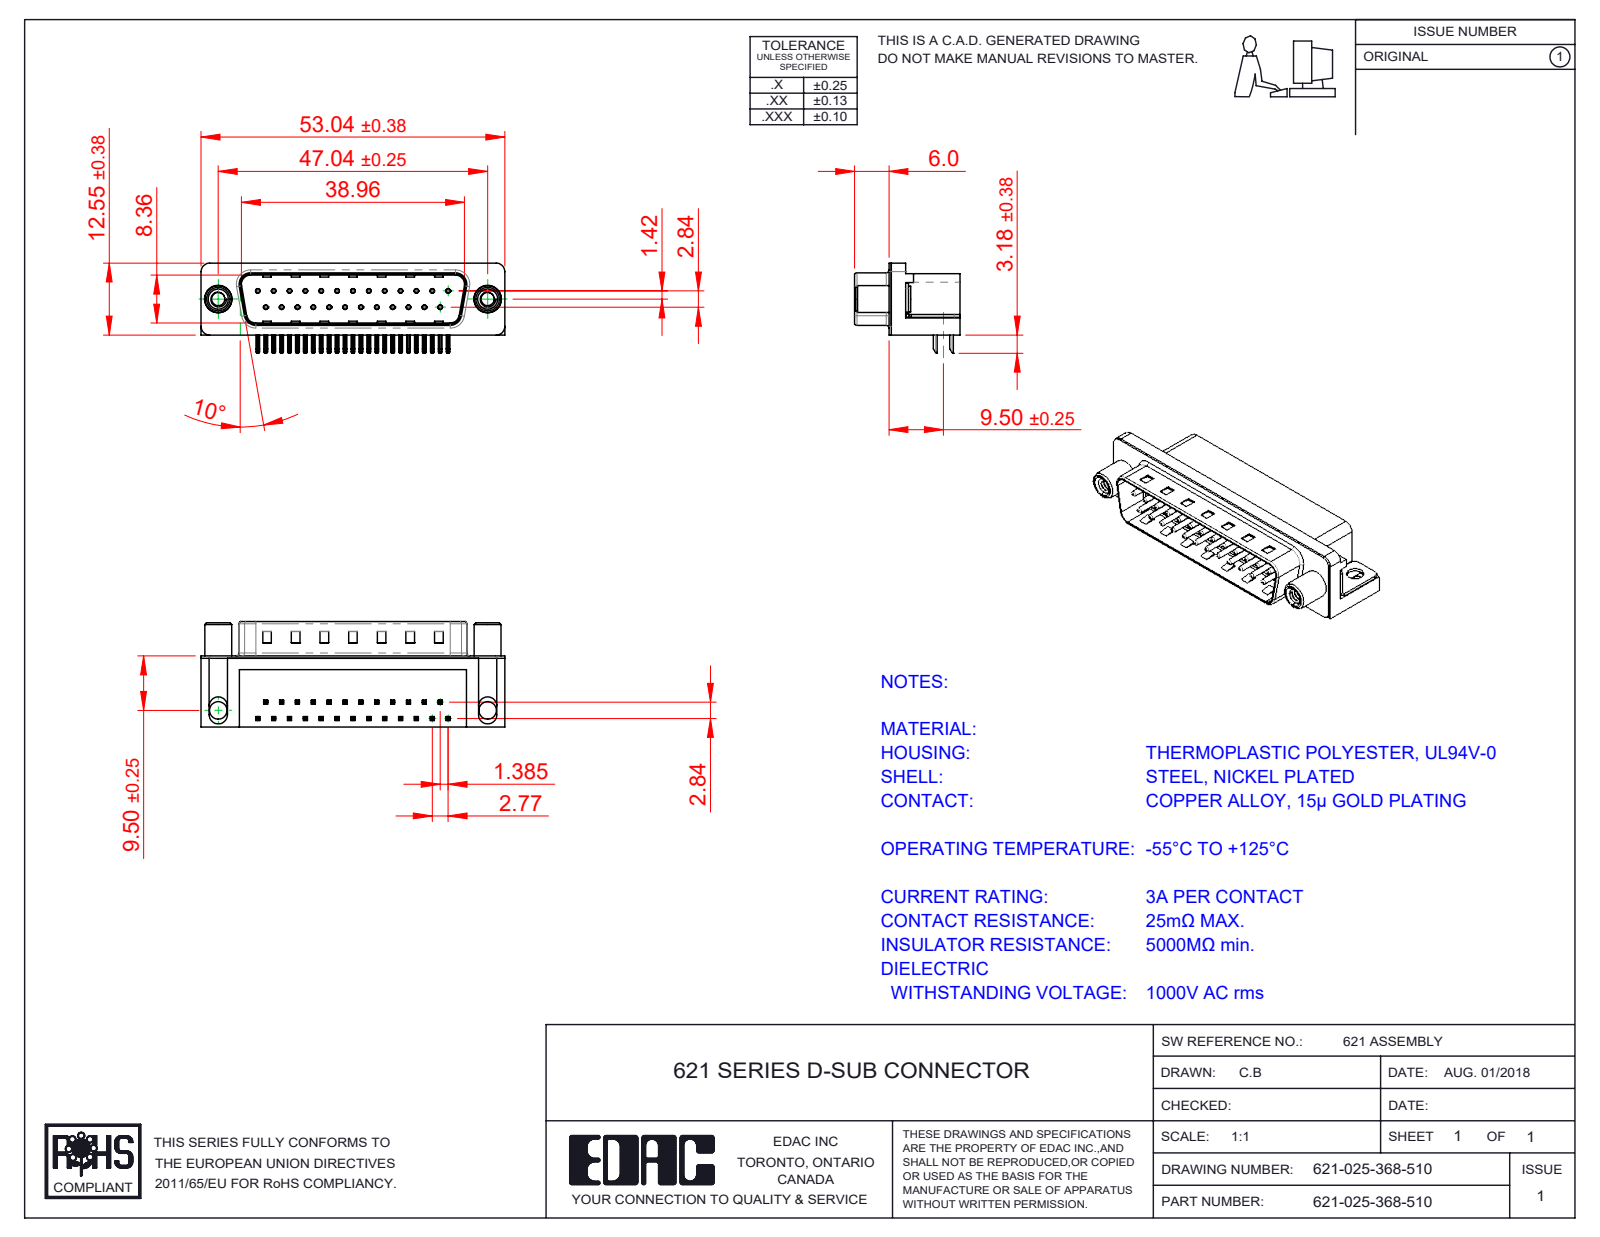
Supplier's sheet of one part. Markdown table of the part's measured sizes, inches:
| quantity | value |
| --- | --- |
| part name | 621-025-368-510; 621 Contact Bottom; 621 Round Threaded Standoff; 621 Thru Hole Board Mount (+3 more) |
| STEP written by | SolidWorks 2016 (CONFIG_CONTROL_DESIGN) |
| units | inches |
| bodies | 31 solids, 2255 faces (1395 planar, 667 cylindrical, 193 other) |
| overall size | 2.088 × 0.724 × 0.619 |
| volume | 0.393 in³ |
| surface area | 12.2 in² |
| round holes (diameter × count) | 0.014 × 25, 0.031 × 25, 0.091 × 2, 0.12 × 2, 0.122 × 2, 0.157 × 2, 0.189 × 2, 0.197 × 2 |
| round bosses / shafts (diameter × count) | 0.03 × 25, 0.193 × 2, 0.185 × 2, 0.177 × 2, 0.152 × 2 |
| partial cylindrical surfaces (radius × count) | 0.01 × 100, 0.005 × 50, 0.039 × 16, 0.02 × 9, 0.063 × 8, 0.059 × 7, 0.035 × 4, 0.079 × 4 |
| main face-to-face distances | 0.016, 0.472, 0.407, 0.083, 0.345, 0.412, 0.067, 0.428, 0.488, 0.114 |
| hole center spacings | 0.124, 0.109, 0.218, 0.327, 0.436, 0.545, 0.654, 0.198 |
